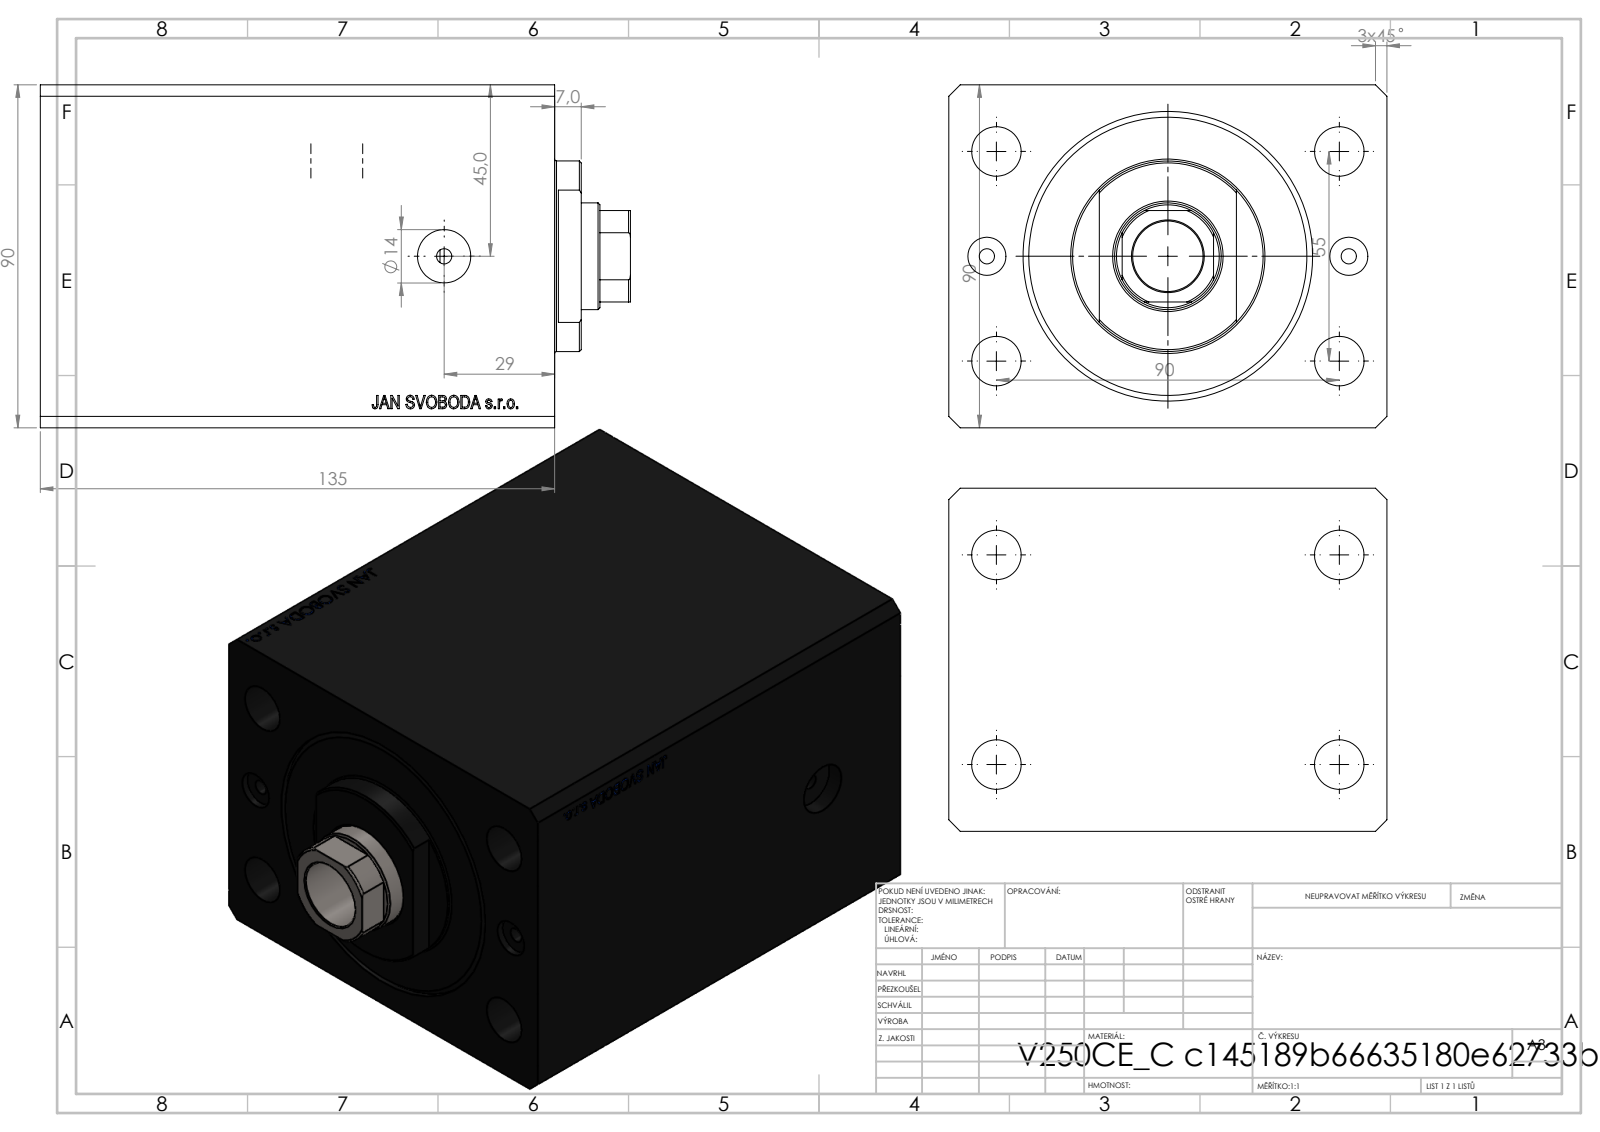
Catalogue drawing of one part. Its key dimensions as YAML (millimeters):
part_name: "V250CE_VC_C; V250CE_C_VCP; V250CE_C_Body"
step_written_by: "SolidWorks 2019 (CONFIG_CONTROL_DESIGN)"
units: millimeters
bodies: {solids: 3, faces: 864, planar: 428, cylindrical: 44, other: 392}
overall_size: [154.9, 115, 90]
volume: 1204000
surface_area: 166122
round_holes:
  - {diameter: 4, count: 4}
  - {diameter: 13, count: 4}
  - {diameter: 10, count: 2}
  - {diameter: 14, count: 2}
  - {diameter: 18.5, count: 1}
  - {diameter: 28, count: 1}
  - {diameter: 63, count: 1}
  - {diameter: 76, count: 1}
round_bosses_or_shafts:
  - {diameter: 50, count: 1}
partial_cylinders:
  - {radius: 13.5, count: 1}
face_to_face_distances: [90, 115, 135, 17.9, 117.1, 104.9, 87, 30.1, 50, 54.9]
hole_center_spacings: [27.61, 52.74, 96.5, 47.5, 55, 90, 105.48, 77]
